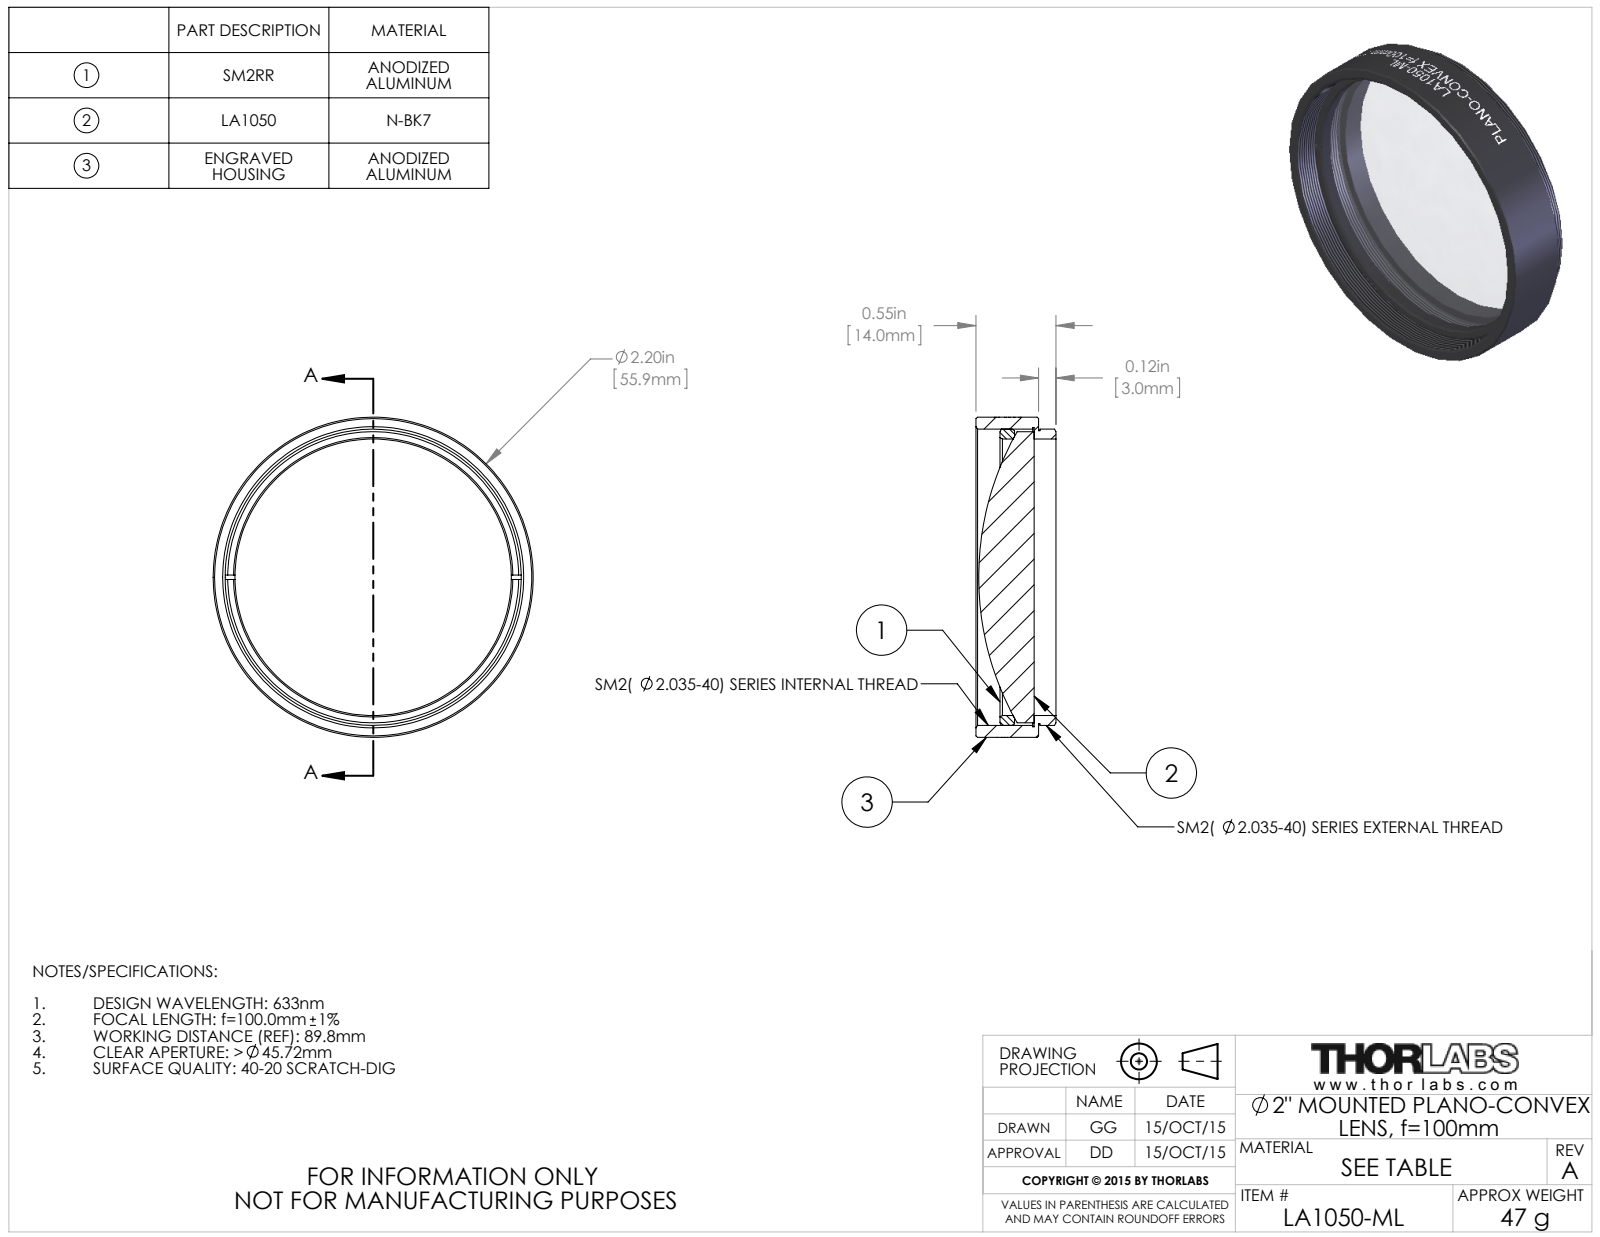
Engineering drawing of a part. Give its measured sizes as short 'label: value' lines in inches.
name: TTN039484-E0W
written by: SolidWorks 2014 (CONFIG_CONTROL_DESIGN)
unit: in
bodies: 3 solids, 109 faces (16 planar, 73 cylindrical, 20 other)
size: 2.2 × 2.2 × 0.55
volume: 1.129 in³; area: 18.34 in²
holes: 1× ⌀1.9, 1× ⌀2.055
bosses: 1× ⌀2.2, 1× ⌀2.035, 1× ⌀2.015, 1× ⌀2
face distances: 0.03, 0.43, 0.4, 0.12, 0.15, 0.55, 0.286, 0.166, 0.136, 0.264
